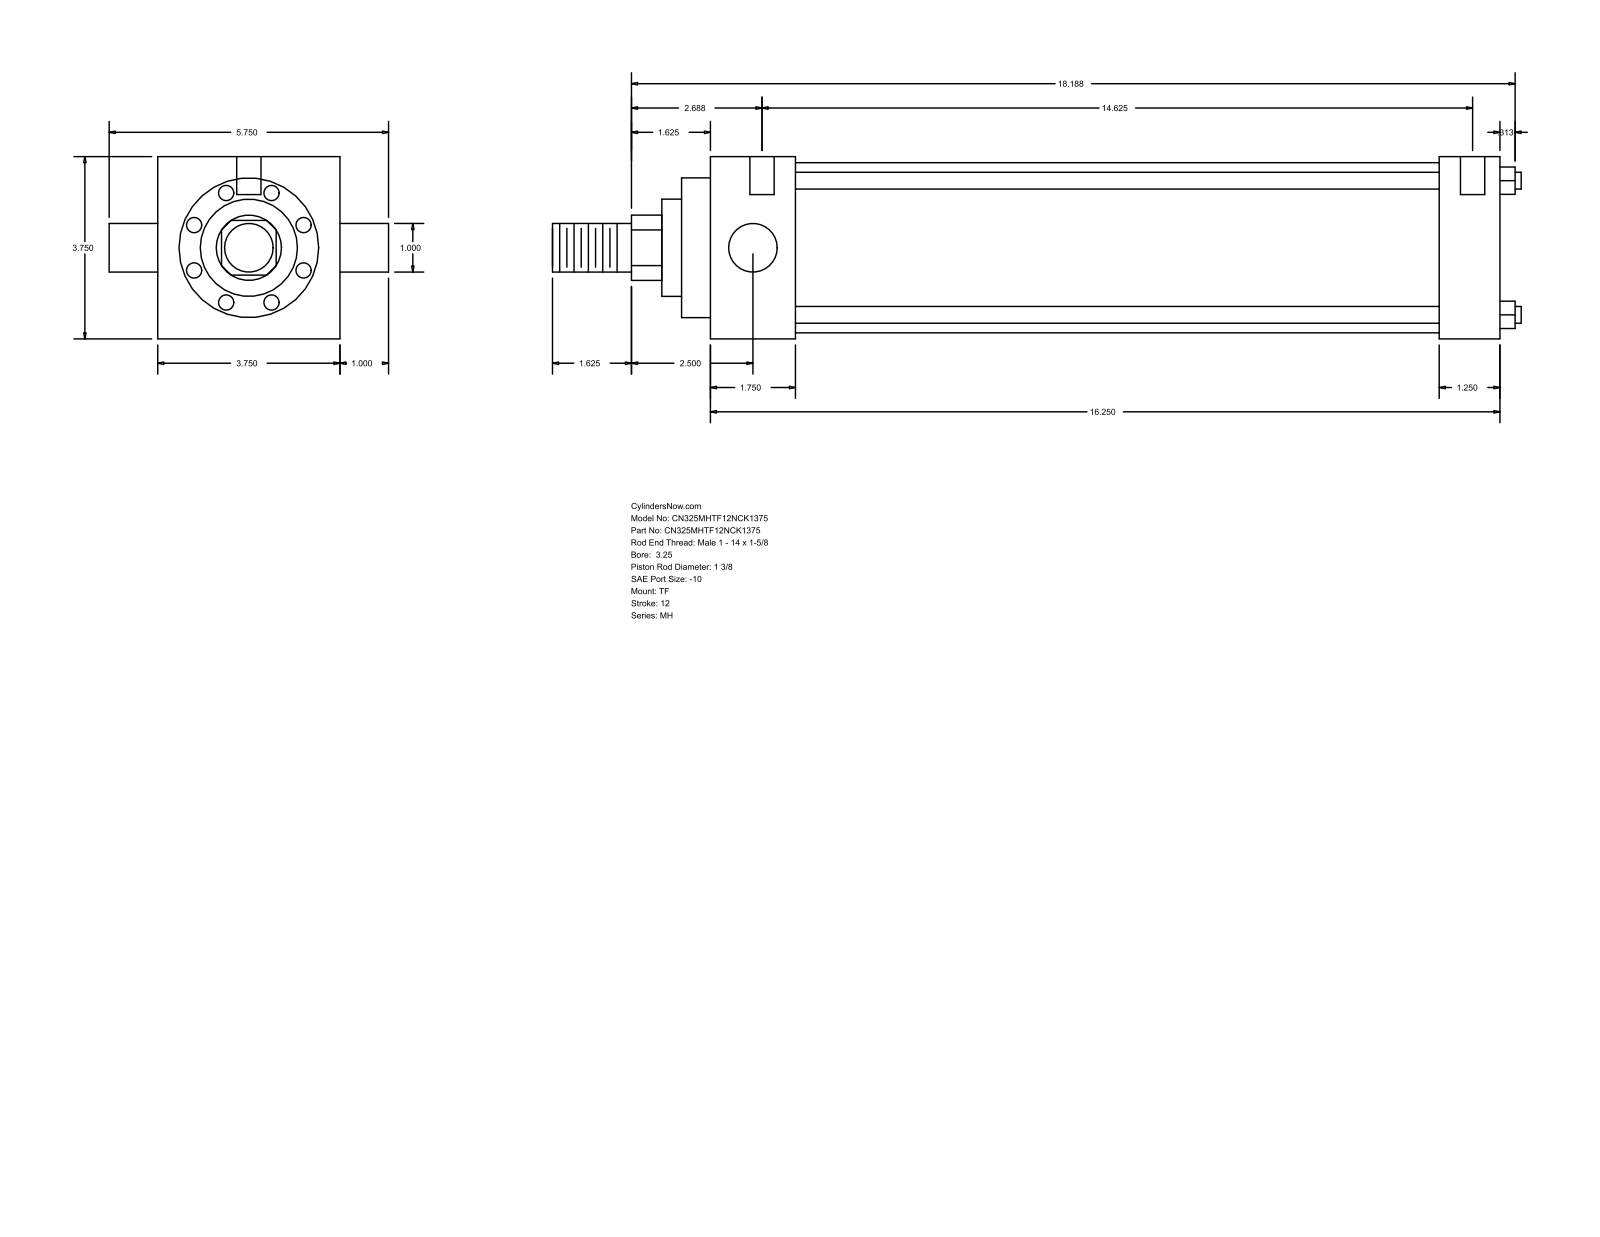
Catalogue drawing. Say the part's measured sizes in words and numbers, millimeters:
The part is named "MH_TF__0325_1.375". Its 3-D file was written by "GSSL Pune (CONFIG_CONTROL_DESIGN)". It is 0 solids with 86 faces: 61 planar, 25 cylindrical and 0 other. Overall it measures 506.41 by 146.05 by 95.25 millimeters. Round holes: 3 of diameter 5.56, 2 of diameter 12.7. Round bosses or shafts: 4 of diameter 8.76, 2 of diameter 25.4, 1 of diameter 88.9, 1 of diameter 73.03, 1 of diameter 50.8, 1 of diameter 34.92. Partial cylindrical surfaces (rounded edges, fillets, slot ends): 1 of radius 17.06. The main face-to-face distances are 95.24, 412.75, 44.45, 381, 336.55, 368.3, 31.75, 15.08, 59.53, 396.08. The hole center spacings are 1.59, 4.76, 371.48, 373.07, 376.24, 377.83.
